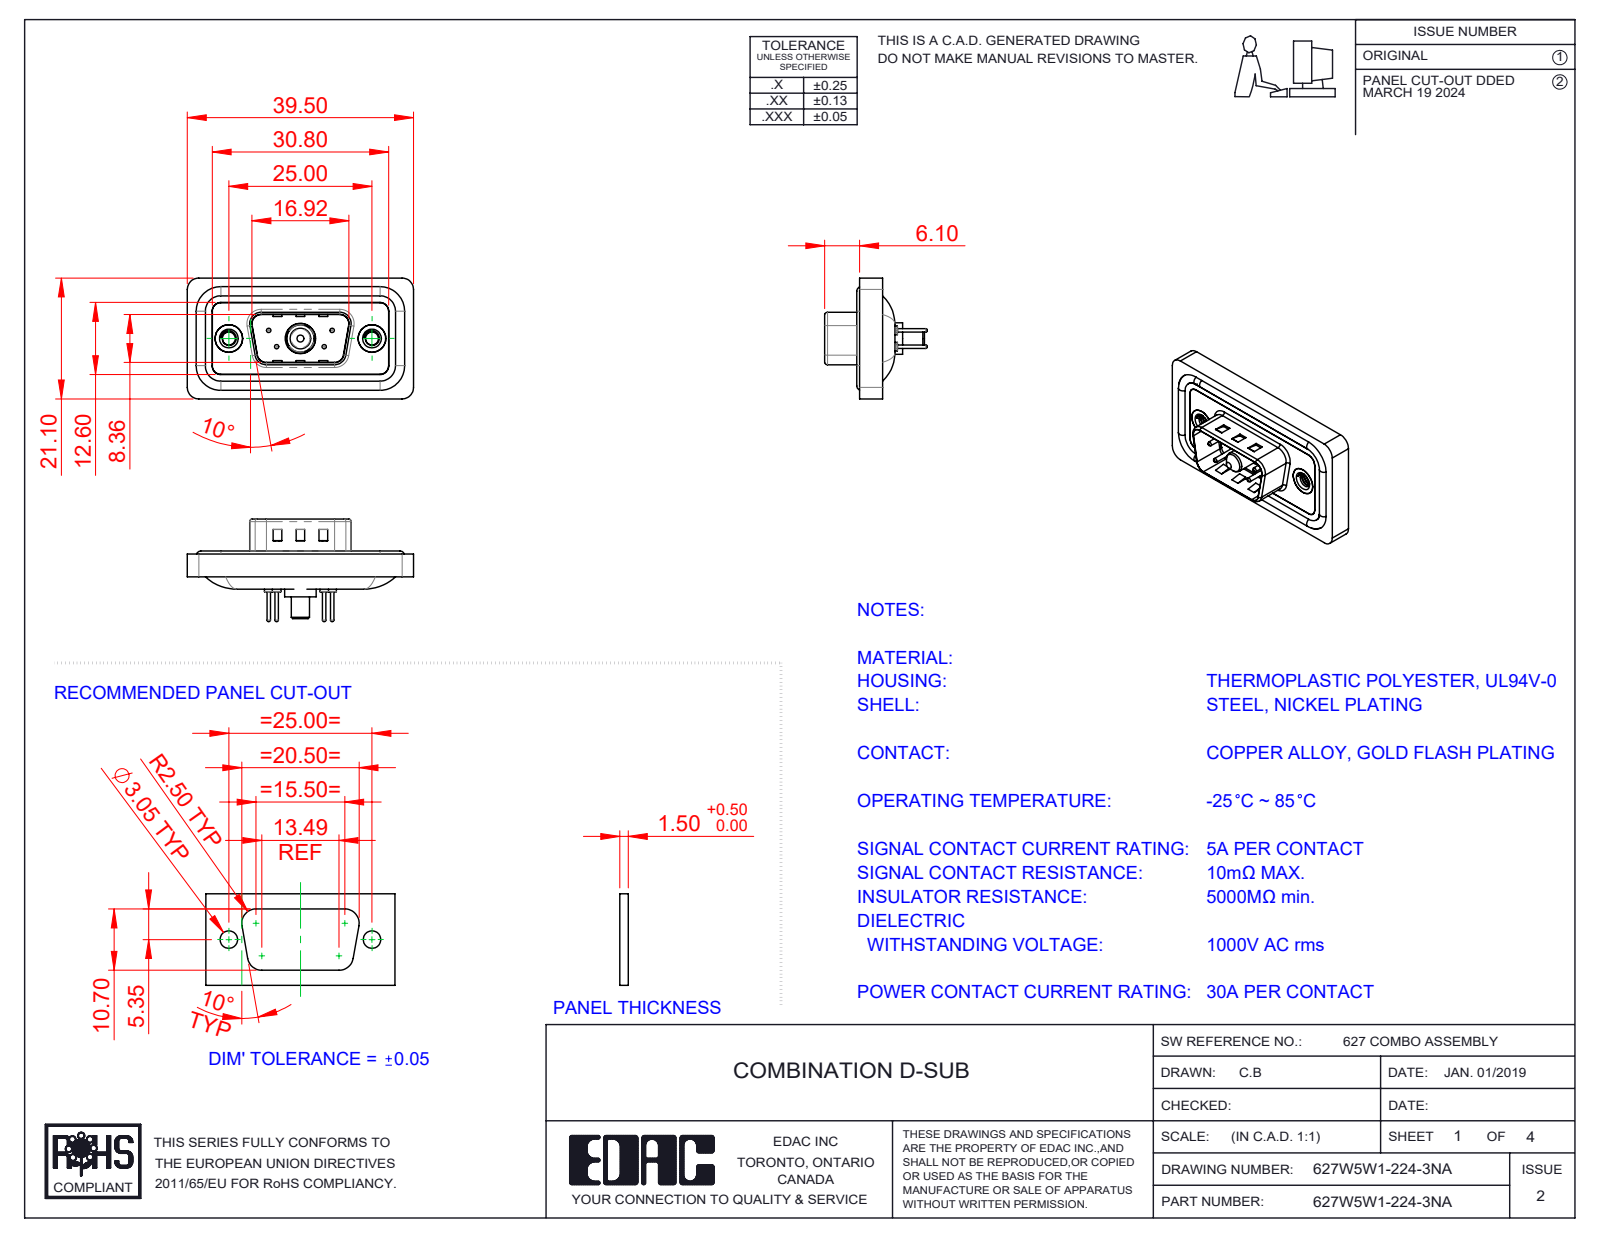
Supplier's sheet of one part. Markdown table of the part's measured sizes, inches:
| quantity | value |
| --- | --- |
| part name | 627Combo Shell Rear_09 Contacts; 627Combo Housing_5W1; 627Combo Waterproof Housing_09 Contacts; 627Combo Contact Row 2_24 (+5 more) |
| STEP written by | SolidWorks 2023 (CONFIG_CONTROL_DESIGN) |
| units | inches |
| bodies | 13 solids, 596 faces (183 planar, 257 cylindrical, 156 other) |
| overall size | 1.555 × 0.831 × 0.705 |
| volume | 0.268 in³ |
| surface area | 10.76 in² |
| round holes (diameter × count) | 0.03 × 4, 0.063 × 4, 0.079 × 4, 0.089 × 2, 0.157 × 2, 0.189 × 2, 0.197 × 2, 0.191 × 1, 0.209 × 1 |
| round bosses / shafts (diameter × count) | 0.063 × 4, 0.059 × 4, 0.024 × 4, 0.193 × 2, 0.217 × 1, 0.205 × 1, 0.187 × 1, 0.148 × 1 |
| partial cylindrical surfaces (radius × count) | 0.059 × 22, 0.079 × 18, 0.02 × 8, 0.063 × 8, 0.01 × 4, 0.024 × 4, 0.026 × 4, 0.035 × 4 |
| main face-to-face distances | 0.016, 0.043, 0.114, 0.063, 0.122, 0.059, 0.02, 0.098, 0.157, 0.031 |
| hole center spacings | 0.124, 0.225, 0.28, 0.492, 0.713, 0.173, 0.173, 0.327 |
